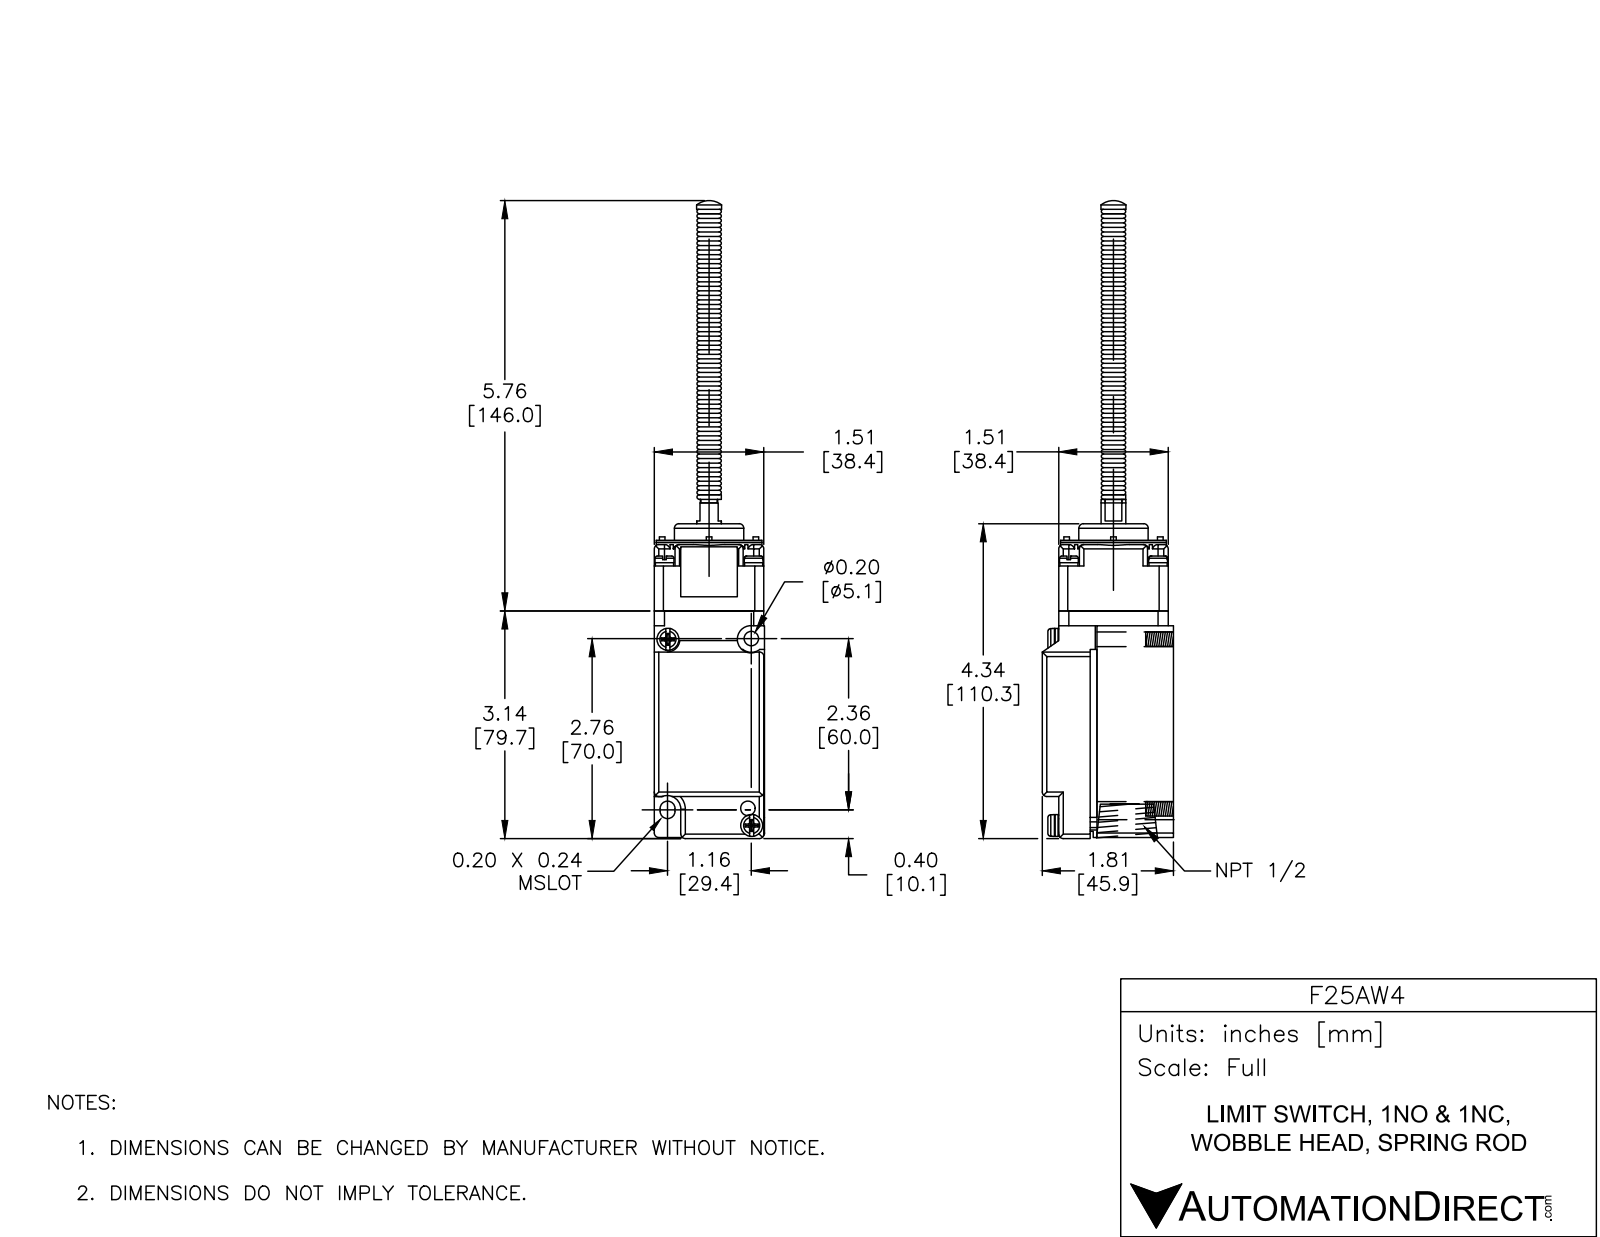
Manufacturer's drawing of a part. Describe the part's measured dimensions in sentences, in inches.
The part is named "F25AW4". Its 3-D file was written by "SolidWorks 2018 (AUTOMOTIVE_DESIGN)". It is 80 solids with 784 faces: 250 planar, 138 cylindrical and 396 other. Overall it measures 8.798 by 1.809 by 1.52 inches. Its volume is 10.12 cubic inches and its surface area 84.77 square inches. Round holes: 4 of diameter 0.077, 4 of diameter 0.177, 3 of diameter 0.19, 3 of diameter 0.2, 1 of diameter 0.23, 1 of diameter 0.92, 1 of diameter 1.054. Round bosses or shafts: 4 of diameter 0.26, 4 of diameter 0.25, 4 of diameter 0.14, 2 of diameter 0.302, 2 of diameter 0.3, 1 of diameter 1.458, 1 of diameter 0.956, 1 of diameter 0.4. Partial cylindrical surfaces (rounded edges, fillets, slot ends): 21 of radius 0.062, 16 of radius 0.03, 8 of radius 0.015, 8 of radius 0.062, 4 of radius 0.14, 4 of radius 0.145, 2 of radius 0.102, 2 of radius 0.188. The main face-to-face distances are 0.094, 1.149, 1.055, 1.52, 0.945, 0.66, 0.754, 1.809, 1.51, 0.433. The hole center spacings are 1.403, 0.616, 0.646, 0.616, 0.87, 0.87, 0.913, 0.914.
